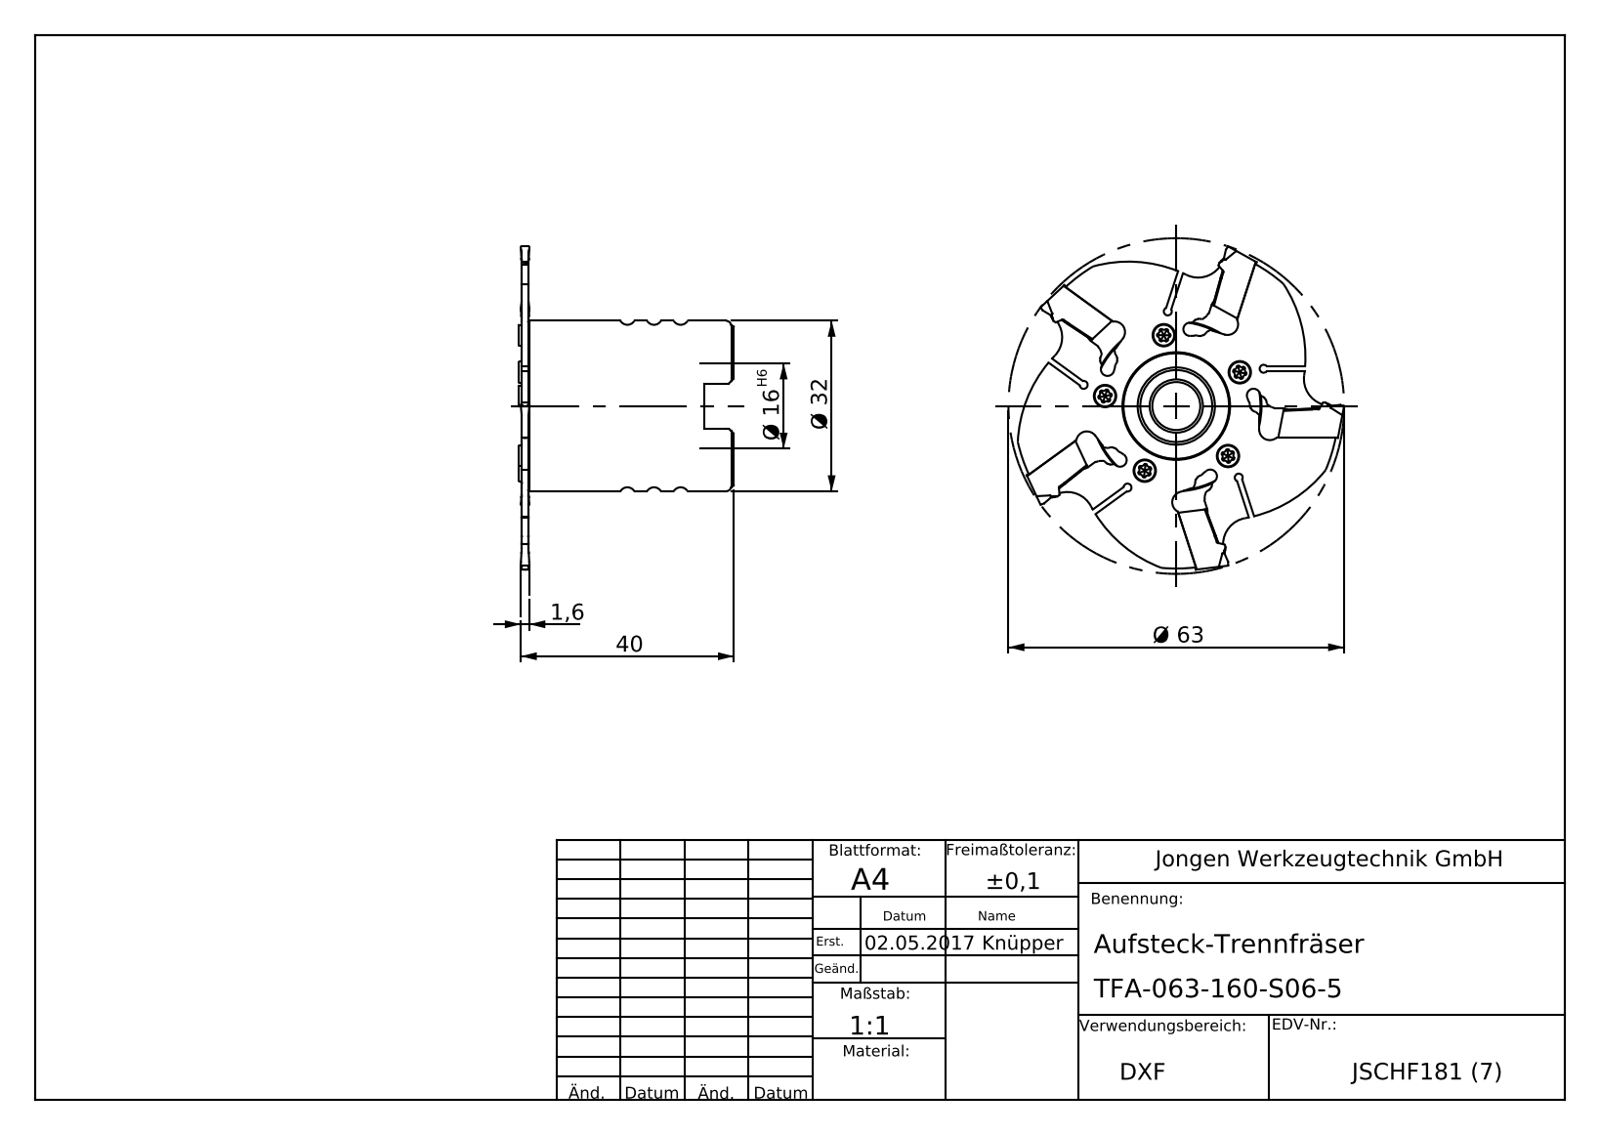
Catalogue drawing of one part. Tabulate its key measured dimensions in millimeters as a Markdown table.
| quantity | value |
| --- | --- |
| part name | TFA-063-160-S06-5; JSCHF181 pk_Kontrolle; JSCHF181_1 pk |
| STEP written by | SolidWorks 2018 (AUTOMOTIVE_DESIGN) |
| units | millimeters |
| bodies | 2 solids, 232 faces (40 planar, 122 cylindrical, 70 other) |
| overall size | 63 × 63 × 40 |
| volume | 27 683 mm³ |
| surface area | 13 395 mm² |
| round holes (diameter × count) | 2.5 × 5, 3.2 × 5, 9 × 1, 13.5 × 1, 16 × 1, 16.15 × 1, 16.3 × 1, 20 × 1, 36.38 × 1 |
| round bosses / shafts (diameter × count) | 63 × 1, 32 × 1 |
| partial cylindrical surfaces (radius × count) | 1 × 20, 2 × 10, 0.75 × 5, 1.25 × 5, 4.64 × 5, 7.14 × 5 |
| main face-to-face distances | 1.6, 1.4, 1.2, 38.4, 38.6, 39.8, 40, 20, 5.6, 32.8 |
| hole center spacings | 13.5, 15.87, 25.68, 25.67, 13.49, 15.86 |
